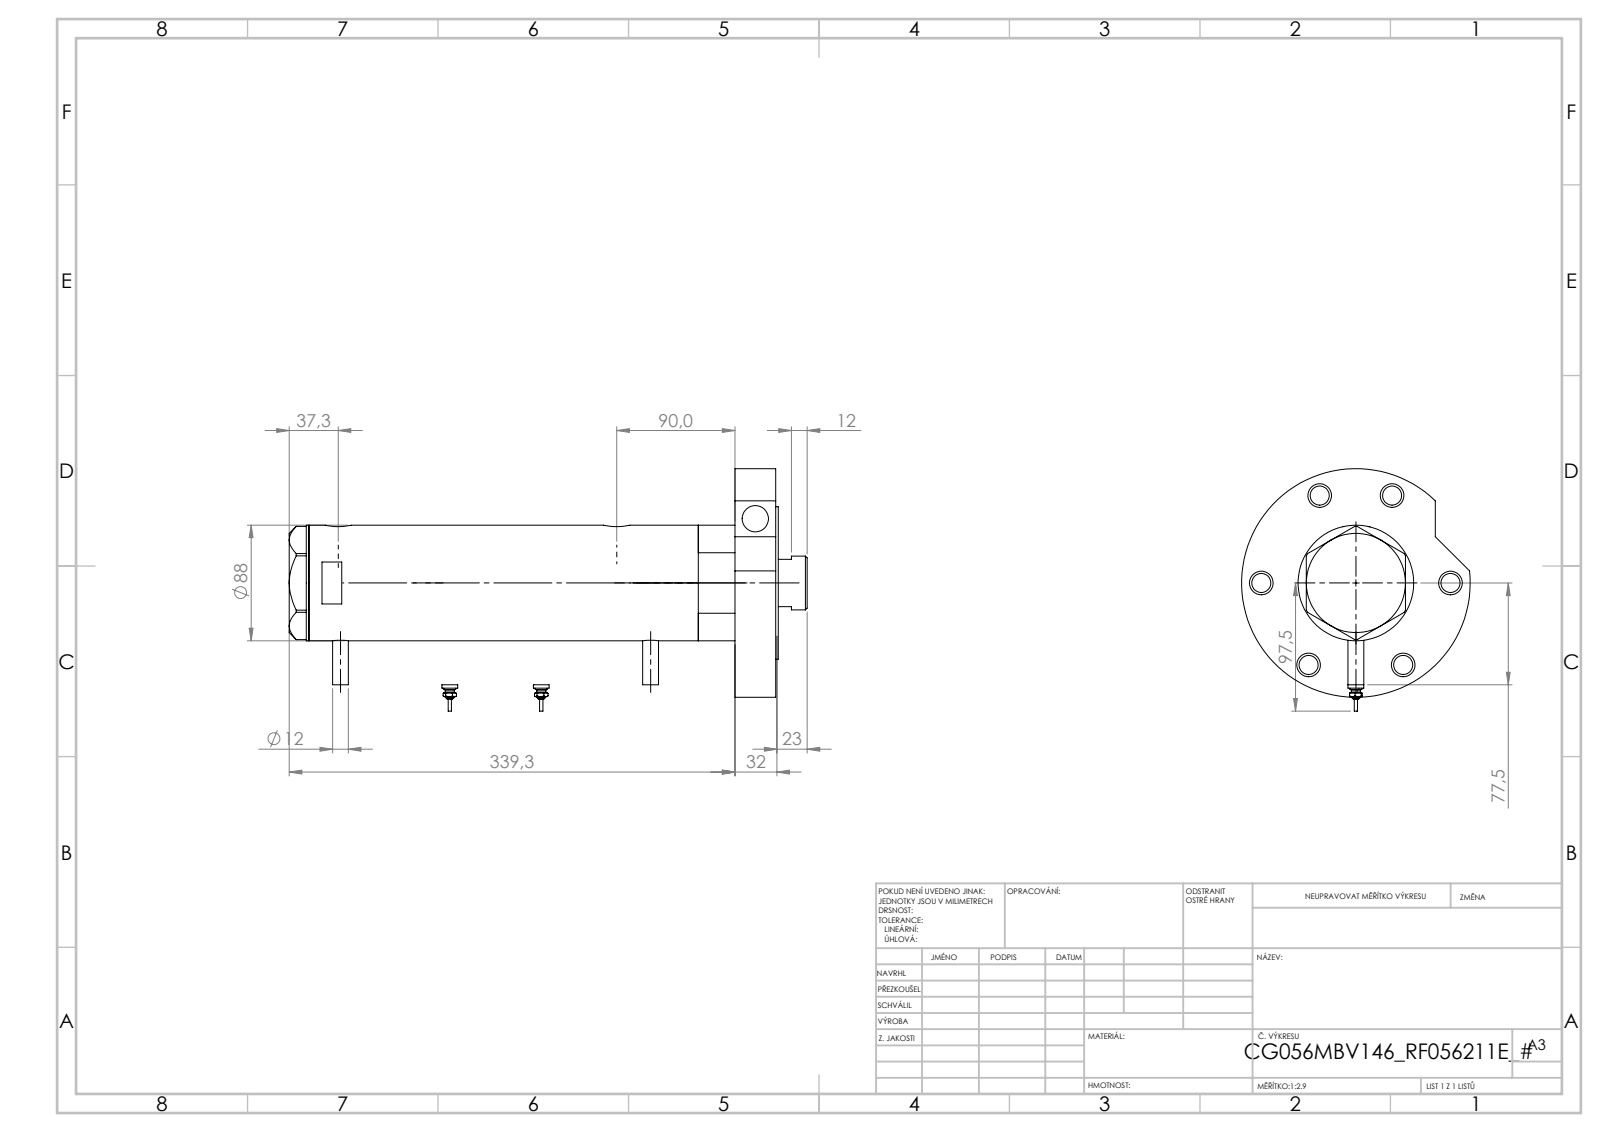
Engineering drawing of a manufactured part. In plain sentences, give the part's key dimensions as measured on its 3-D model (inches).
The part is named "V270CG_FRONT; V270CG_MIDDLE; V270CG_VC; V270CG_BACK (+2 more)". Its 3-D file was written by "SolidWorks 2019 (CONFIG_CONTROL_DESIGN)". It is 7 solids with 257 faces: 91 planar, 102 cylindrical and 64 other. Overall it measures 15.524 by 7.264 by 6.85 inches. Its volume is 156.5 cubic inches and its surface area 559.3 square inches. Round holes: 7 of diameter 0.571, 6 of diameter 0.709, 3 of diameter 0.787, 2 of diameter 0.492, 2 of diameter 0.518, 1 of diameter 1.654, 1 of diameter 1.713, 1 of diameter 2.205, 1 of diameter 2.362, 1 of diameter 2.953, 1 of diameter 3.15. Round bosses or shafts: 4 of diameter 0.472, 2 of diameter 0.354, 2 of diameter 0.276, 2 of diameter 0.177, 2 of diameter 0.098, 1 of diameter 6.85, 1 of diameter 4.567, 1 of diameter 3.465. The main face-to-face distances are 1.22, 0.079, 14.067, 12.768, 13.988, 1.299, 9.228, 3.539, 4.76, 4.839. The hole center spacings are 2.835, 3.15, 4.714, 4.91, 5.085, 5.657, 0.067, 1.016.
